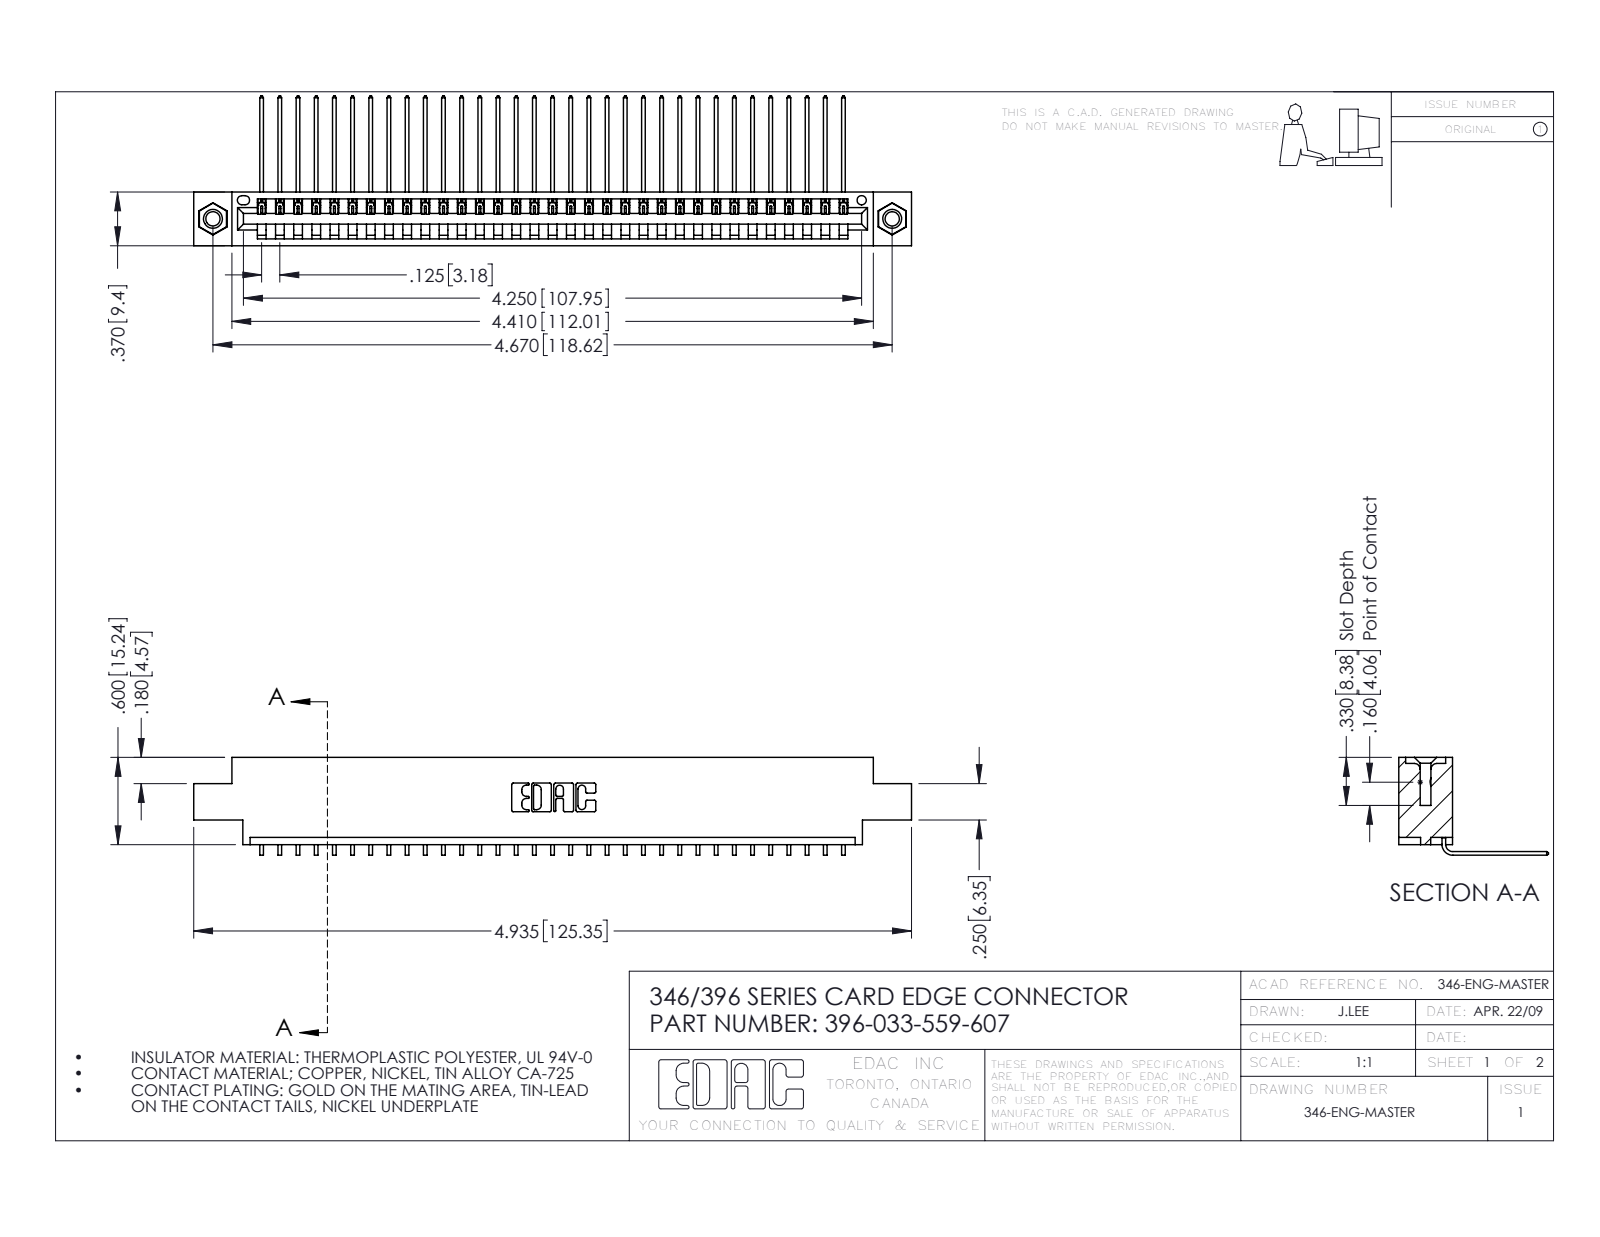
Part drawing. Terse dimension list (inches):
name: 345-292-001_558 559 Tail - 1; 346 Part_0.170 Offset - 0.156 Dia-TI; 396-033-559-607; 345-250-001_345-250-005-103
written by: SolidWorks 2016 (CONFIG_CONTROL_DESIGN)
unit: in
bodies: 36 solids, 2166 faces (1498 planar, 652 cylindrical, 16 other)
size: 4.935 × 1.03 × 0.673
volume: 0.725 in³; area: 24.18 in²
holes: 2× ⌀0.098, 2× ⌀0.125, 2× ⌀0.156, 1× ⌀0.064
bosses: 2× ⌀0.155
rounds: 66× R0.006, 22× R0.01, 6× R0.007, 6× R0.031, 3× R0.026, 2× R0.031, 2× R0.04, 1× R0.014
face distances: 0.048, 0.322, 0.37, 0.025, 0.25, 0.072, 0.222, 0.148, 0.298, 0.1
hole spacings: 0.246, 4.462, 4.67
